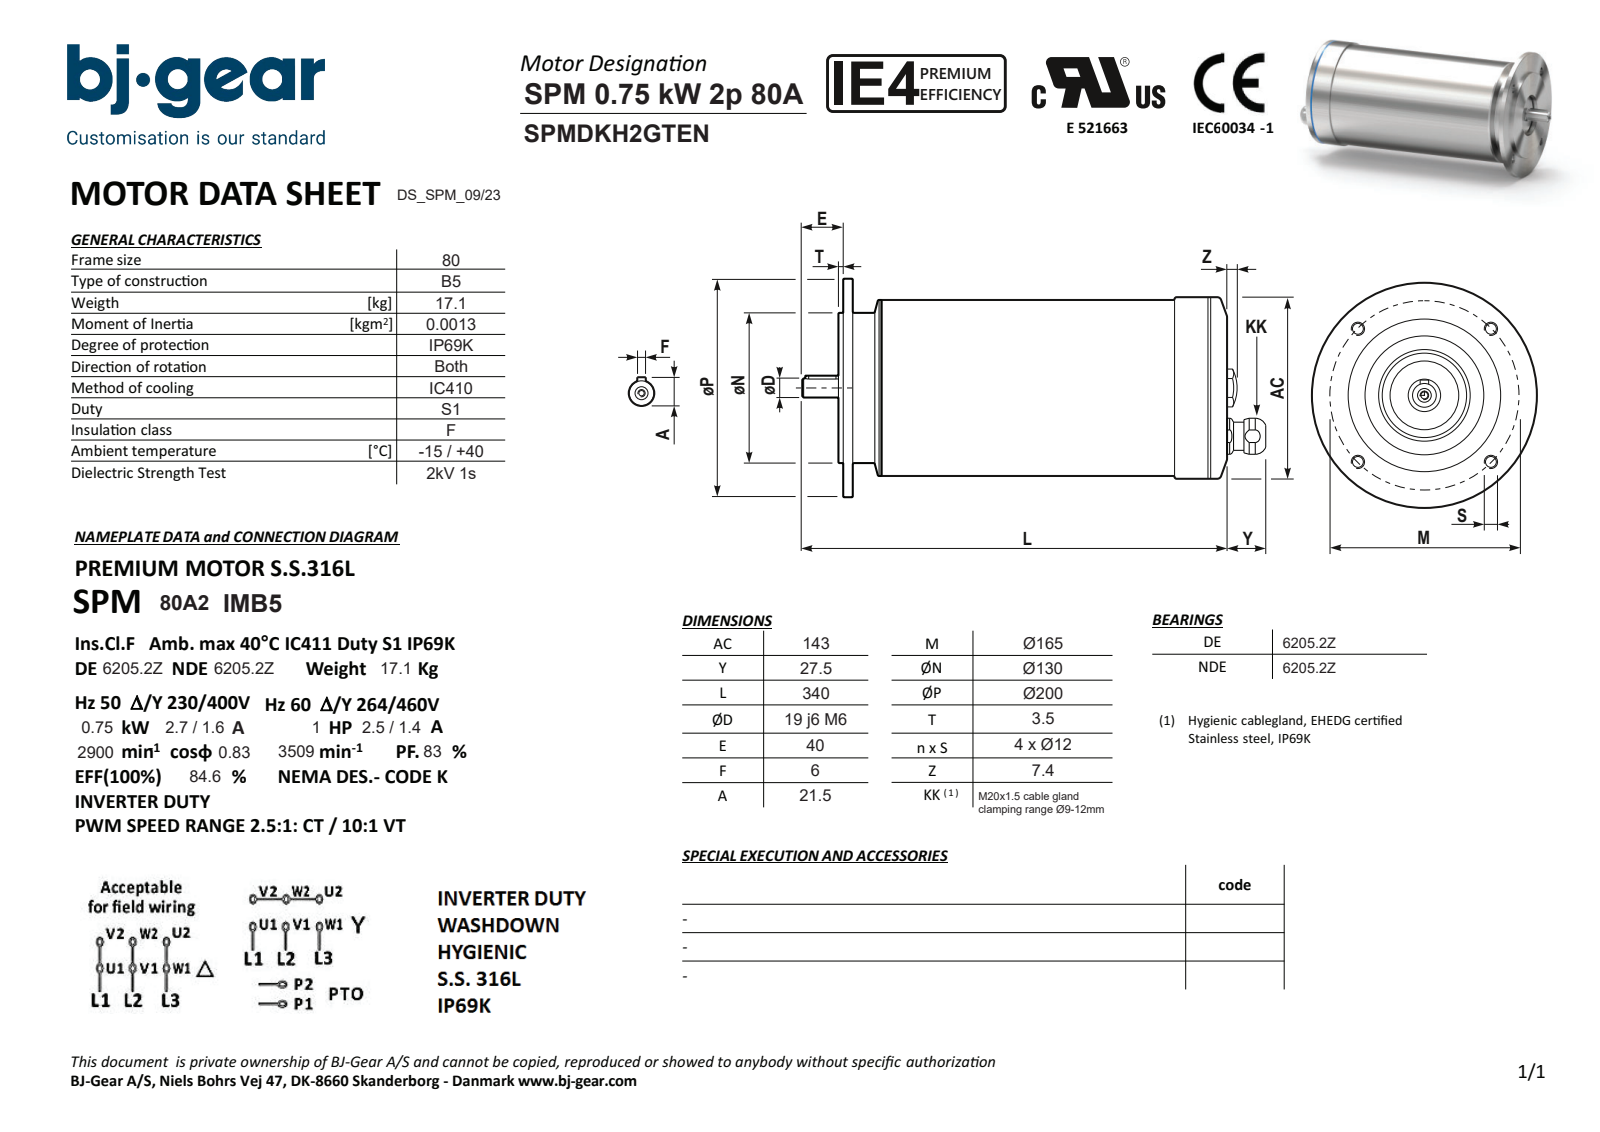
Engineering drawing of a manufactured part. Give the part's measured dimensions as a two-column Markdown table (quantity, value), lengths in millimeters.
| quantity | value |
| --- | --- |
| part name | SPMDKH2GTENN4KSA1-N---NNN |
| STEP written by | Solid Edge (AUTOMOTIVE_DESIGN) |
| units | millimeters |
| bodies | 1 solid, 79 faces (30 planar, 28 cylindrical, 21 other) |
| overall size | 367.5 × 200 × 200 |
| volume | 4 736 000 mm³ |
| surface area | 203 697 mm² |
| round holes (diameter × count) | 12 × 4, 4.92 × 1, 6.4 × 1, 7 × 1, 13.4 × 1, 68 × 1 |
| round bosses / shafts (diameter × count) | 200 × 1, 143 × 1, 142.98 × 1, 139 × 1, 138.98 × 1, 130 × 1, 25 × 1, 20 × 1 |
| partial cylindrical surfaces (radius × count) | 3 × 2, 12.8 × 1 |
| main face-to-face distances | 8, 11.5, 3.5, 292, 300, 303.5, 6, 2, 294, 9.5 |
| hole center spacings | 82.51, 116.68, 61.78, 112.63, 165.01, 38 |
